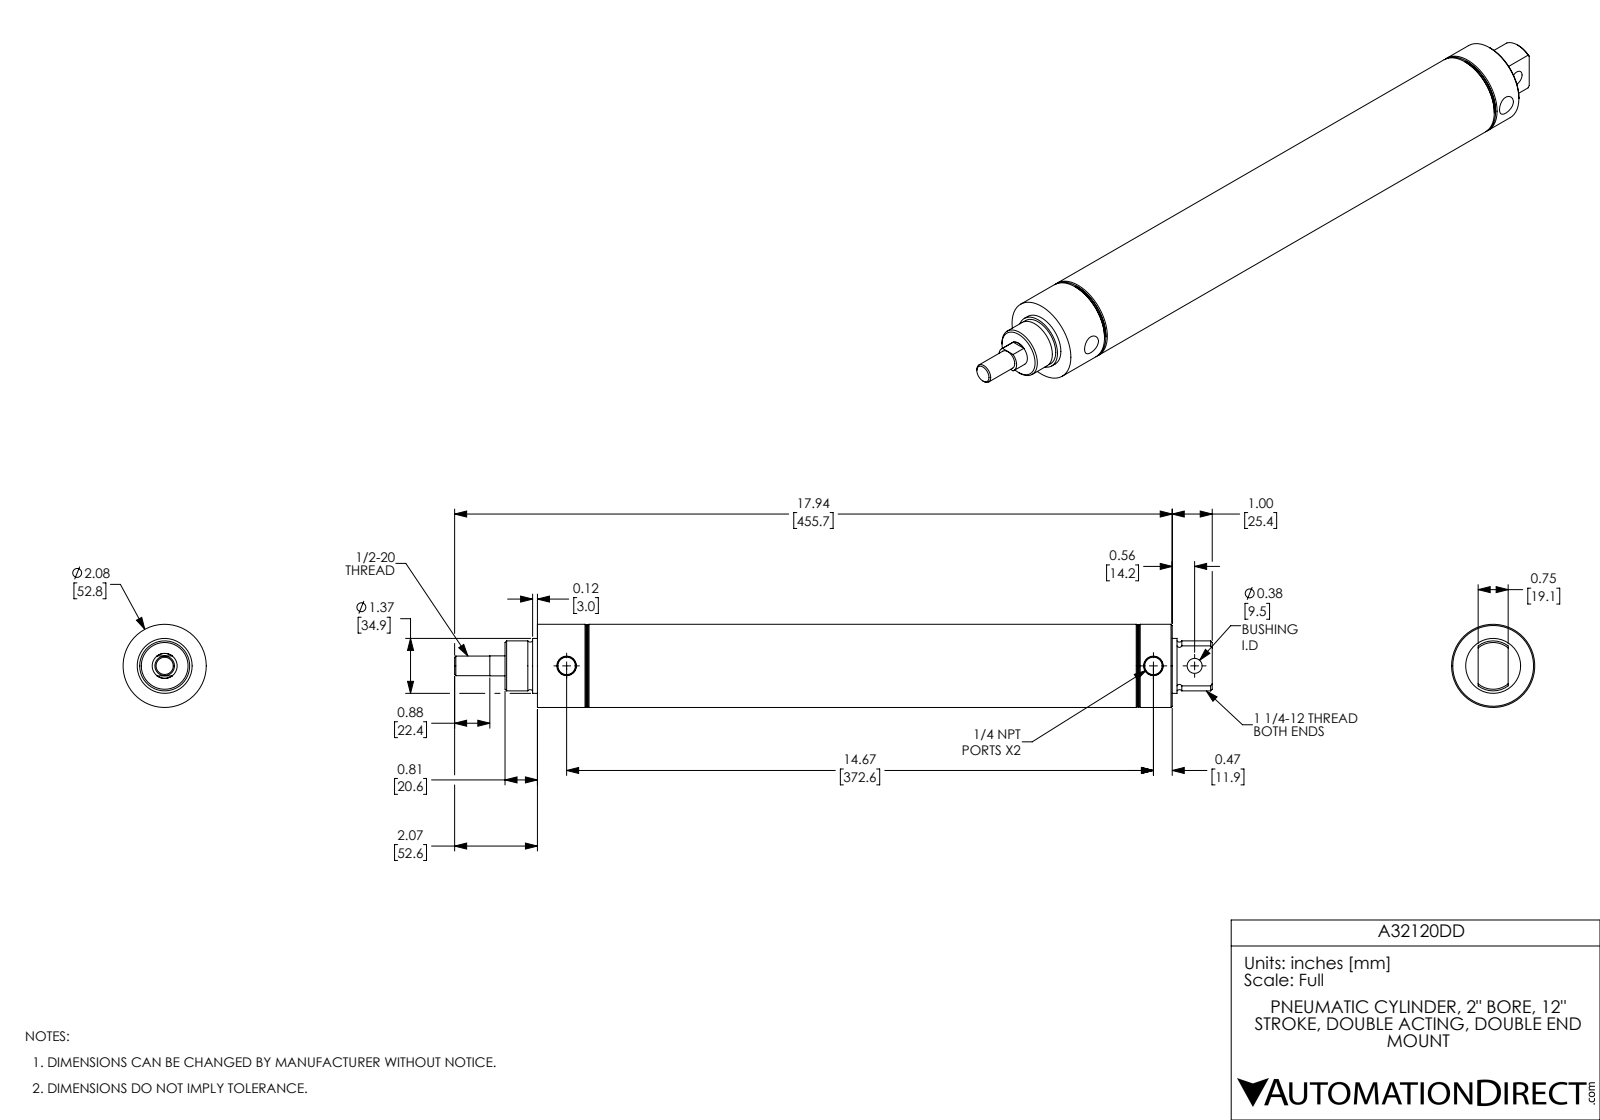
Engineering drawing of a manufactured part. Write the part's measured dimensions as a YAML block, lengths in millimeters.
part_name: "A32120DD; A32120DD-Rod; A32120DD-MainBody"
step_written_by: "SolidWorks 2017 (AUTOMOTIVE_DESIGN)"
units: millimeters
bodies: {solids: 2, faces: 88, planar: 20, cylindrical: 30, other: 38}
overall_size: [481.1, 52.8, 52.8]
volume: 356300
surface_area: 161000
round_holes:
  - {diameter: 11.1, count: 2}
  - {diameter: 9.5, count: 1}
  - {diameter: 15.9, count: 1}
  - {diameter: 50.8, count: 1}
round_bosses_or_shafts:
  - {diameter: 52.8, count: 1}
  - {diameter: 34.9, count: 1}
  - {diameter: 31.8, count: 1}
  - {diameter: 12.5, count: 1}
face_to_face_distances: [12.7, 317.5, 304.8, 360.3, 347.6, 42.8, 42.8, 55.5, 360.3, 403.1]
hole_center_spacings: [26.2, 372.6, 398.8]
